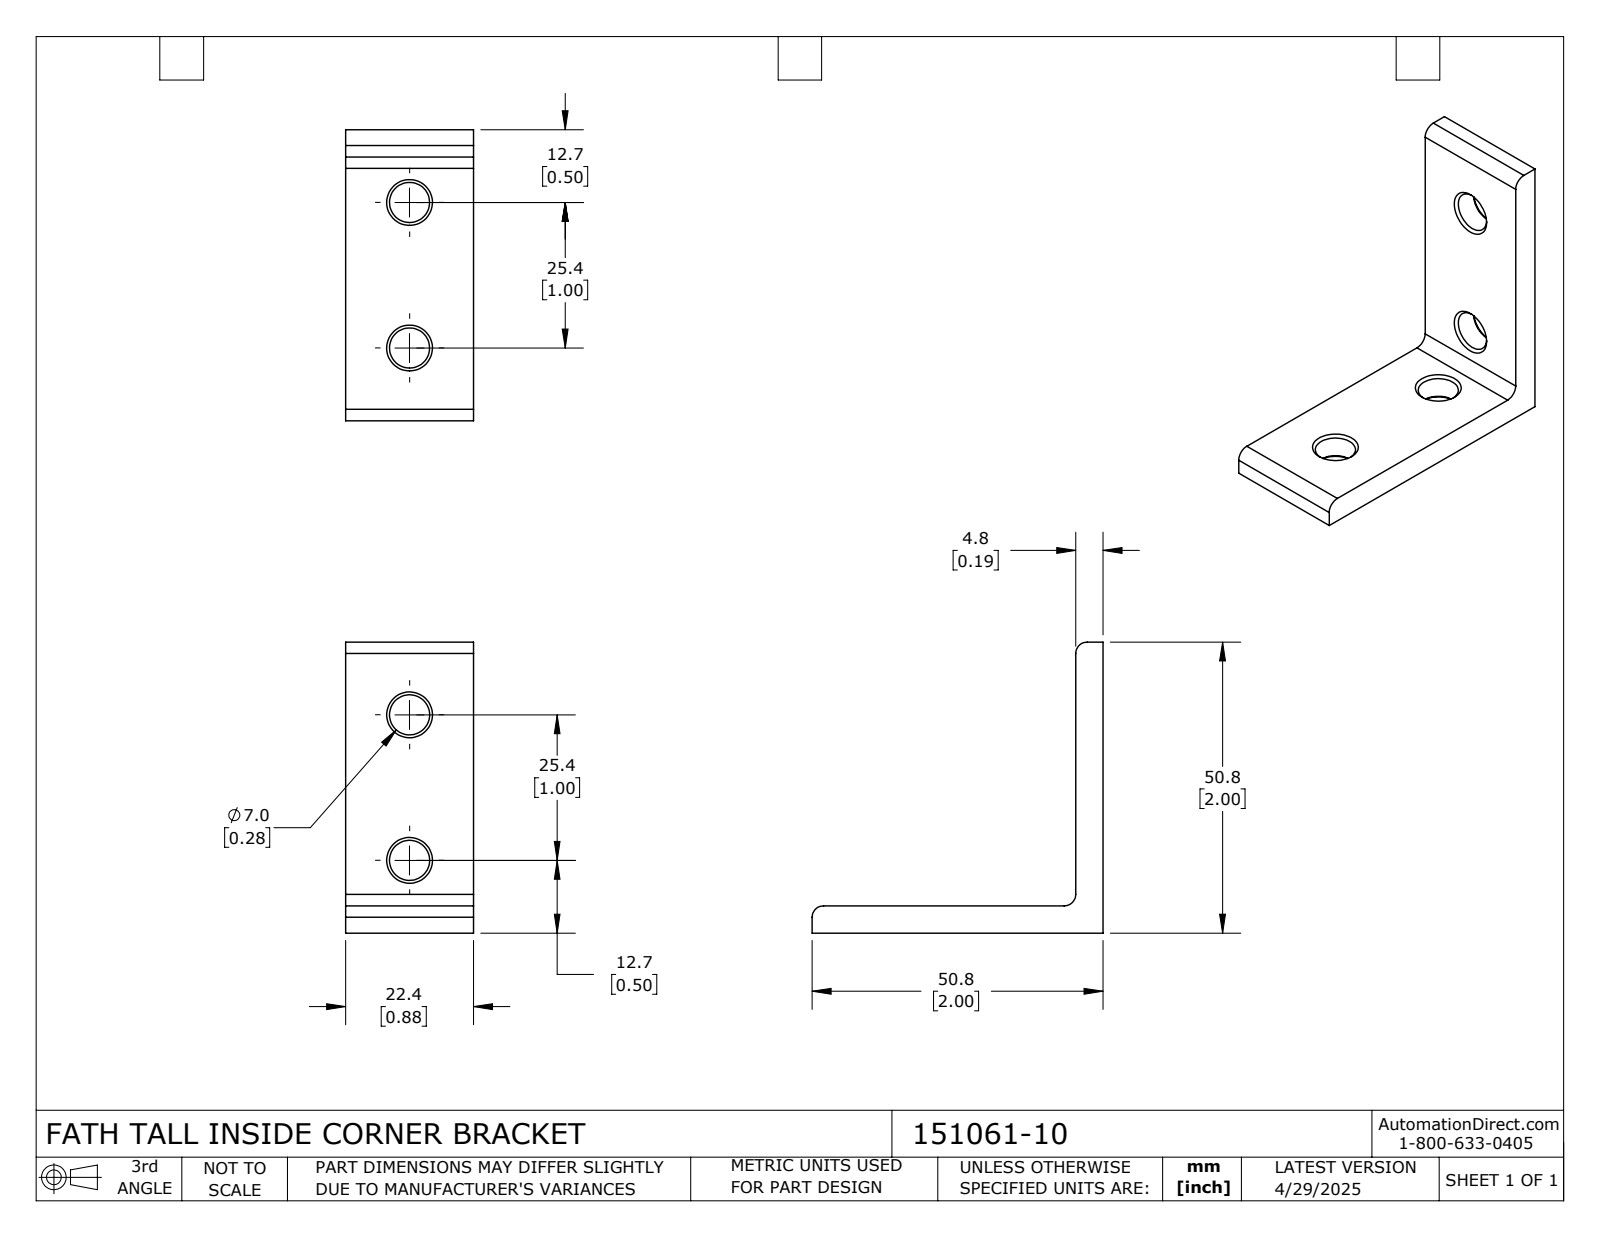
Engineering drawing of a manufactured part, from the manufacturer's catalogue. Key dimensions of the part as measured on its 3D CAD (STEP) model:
Part name (STEP PRODUCT): 151061-10
STEP written by: SolidWorks 2024 (CONFIG_CONTROL_DESIGN)
Units: inches
Bodies: 1 solid, 35 faces (8 planar, 11 cylindrical, 16 other)
Overall size (bounding box): 2 × 2 × 0.88
Volume: 0.582 in³ · Surface area: 8.474 in²
Round holes (diameter × count): ⌀0.276 ×4
Partial cylindrical surfaces — rounded edges, fillets, slot ends (radius × count): R0.079 ×3
Main face-to-face distances: 0.187, 0.88, 2, 1.813
Hole centre spacings: 1
